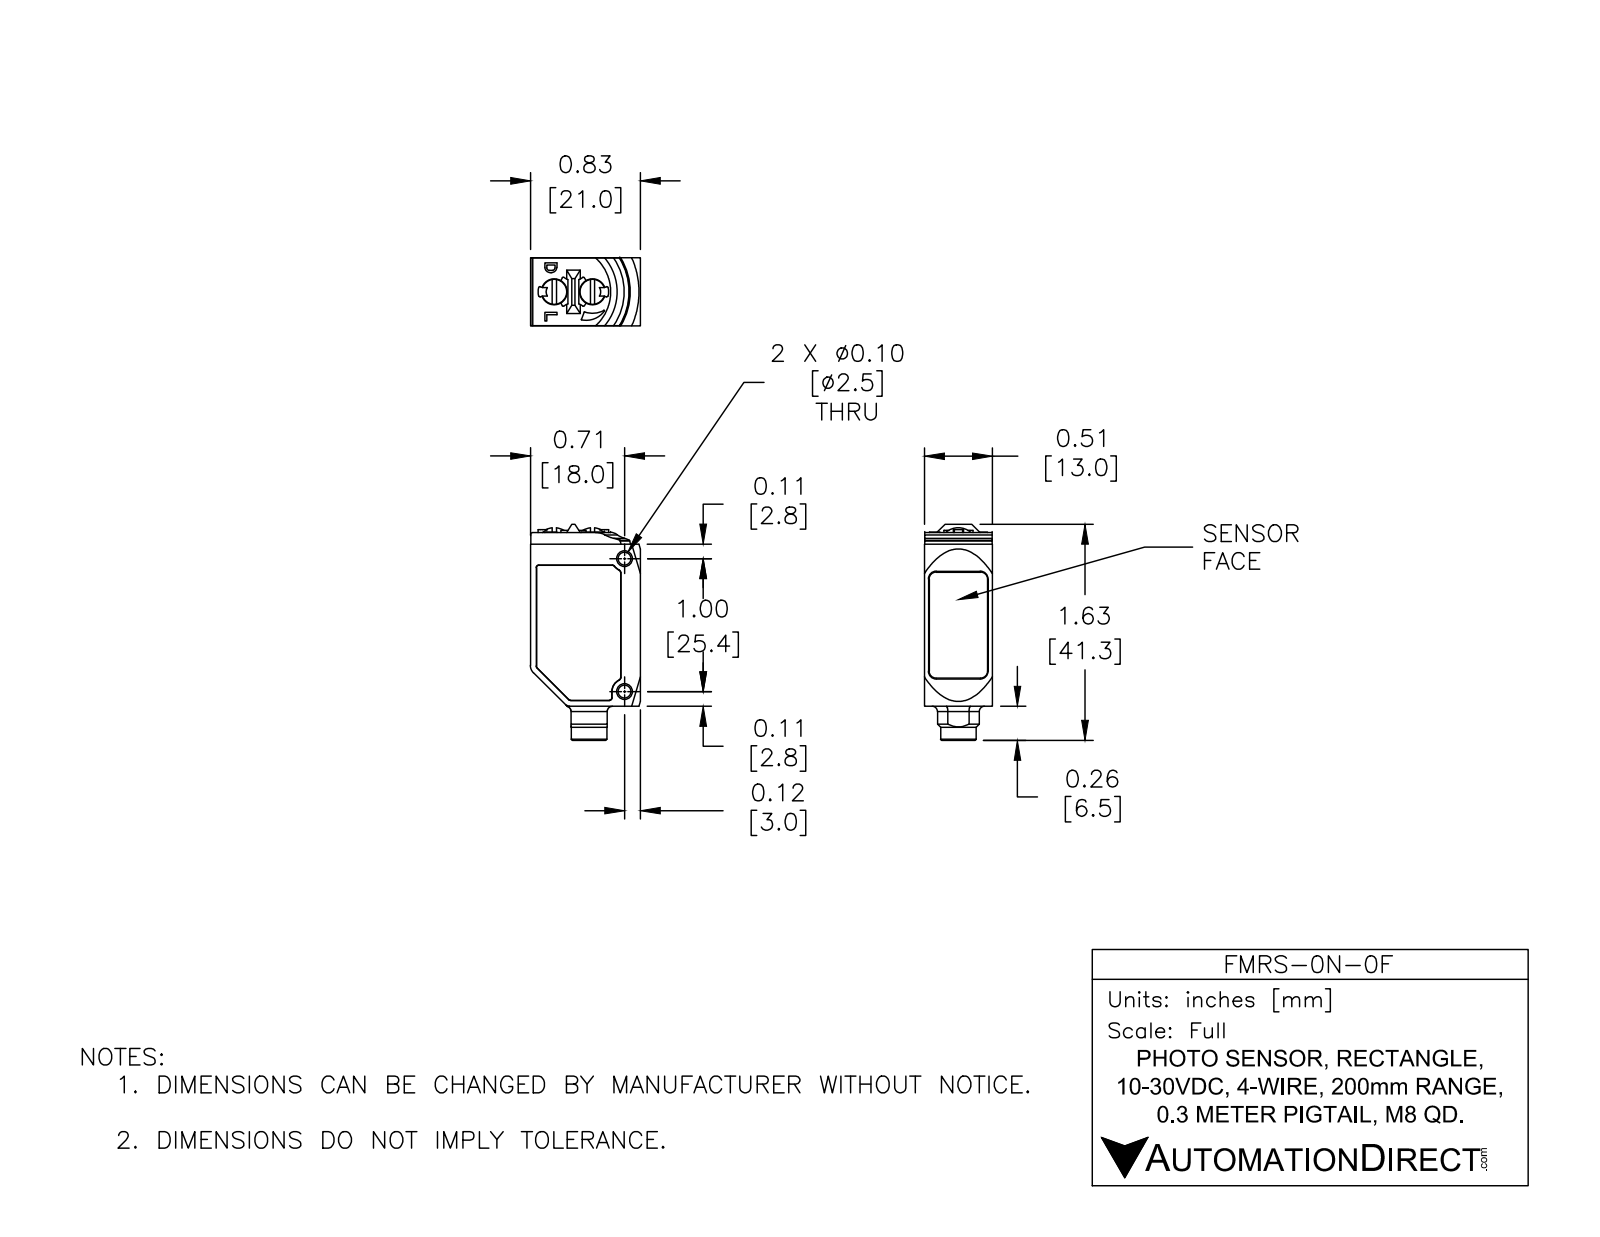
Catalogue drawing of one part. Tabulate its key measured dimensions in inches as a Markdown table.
| quantity | value |
| --- | --- |
| part name | FMRS-0N-0F |
| STEP written by | SolidWorks 2017 (AUTOMOTIVE_DESIGN) |
| units | inches |
| bodies | 1 solid, 197 faces (89 planar, 79 cylindrical, 29 other) |
| overall size | 1.626 × 0.827 × 0.512 |
| volume | 0.527 in³ |
| surface area | 5.26 in² |
| round holes (diameter × count) | 0.097 × 2, 0.197 × 2, 0.228 × 1 |
| round bosses / shafts (diameter × count) | 0.189 × 2, 0.267 × 1 |
| partial cylindrical surfaces (radius × count) | 0.018 × 7, 0.02 × 7, 0.039 × 5, 0.008 × 4, 0.01 × 4, 0.051 × 4, 0.059 × 4, 0.004 × 3 |
| main face-to-face distances | 0.512, 0.827, 1.307, 0.51, 0.031, 0.48, 0.037, 0.035, 0.474, 0.03 |
| hole center spacings | 0.026, 0.262, 0.287, 1 |
